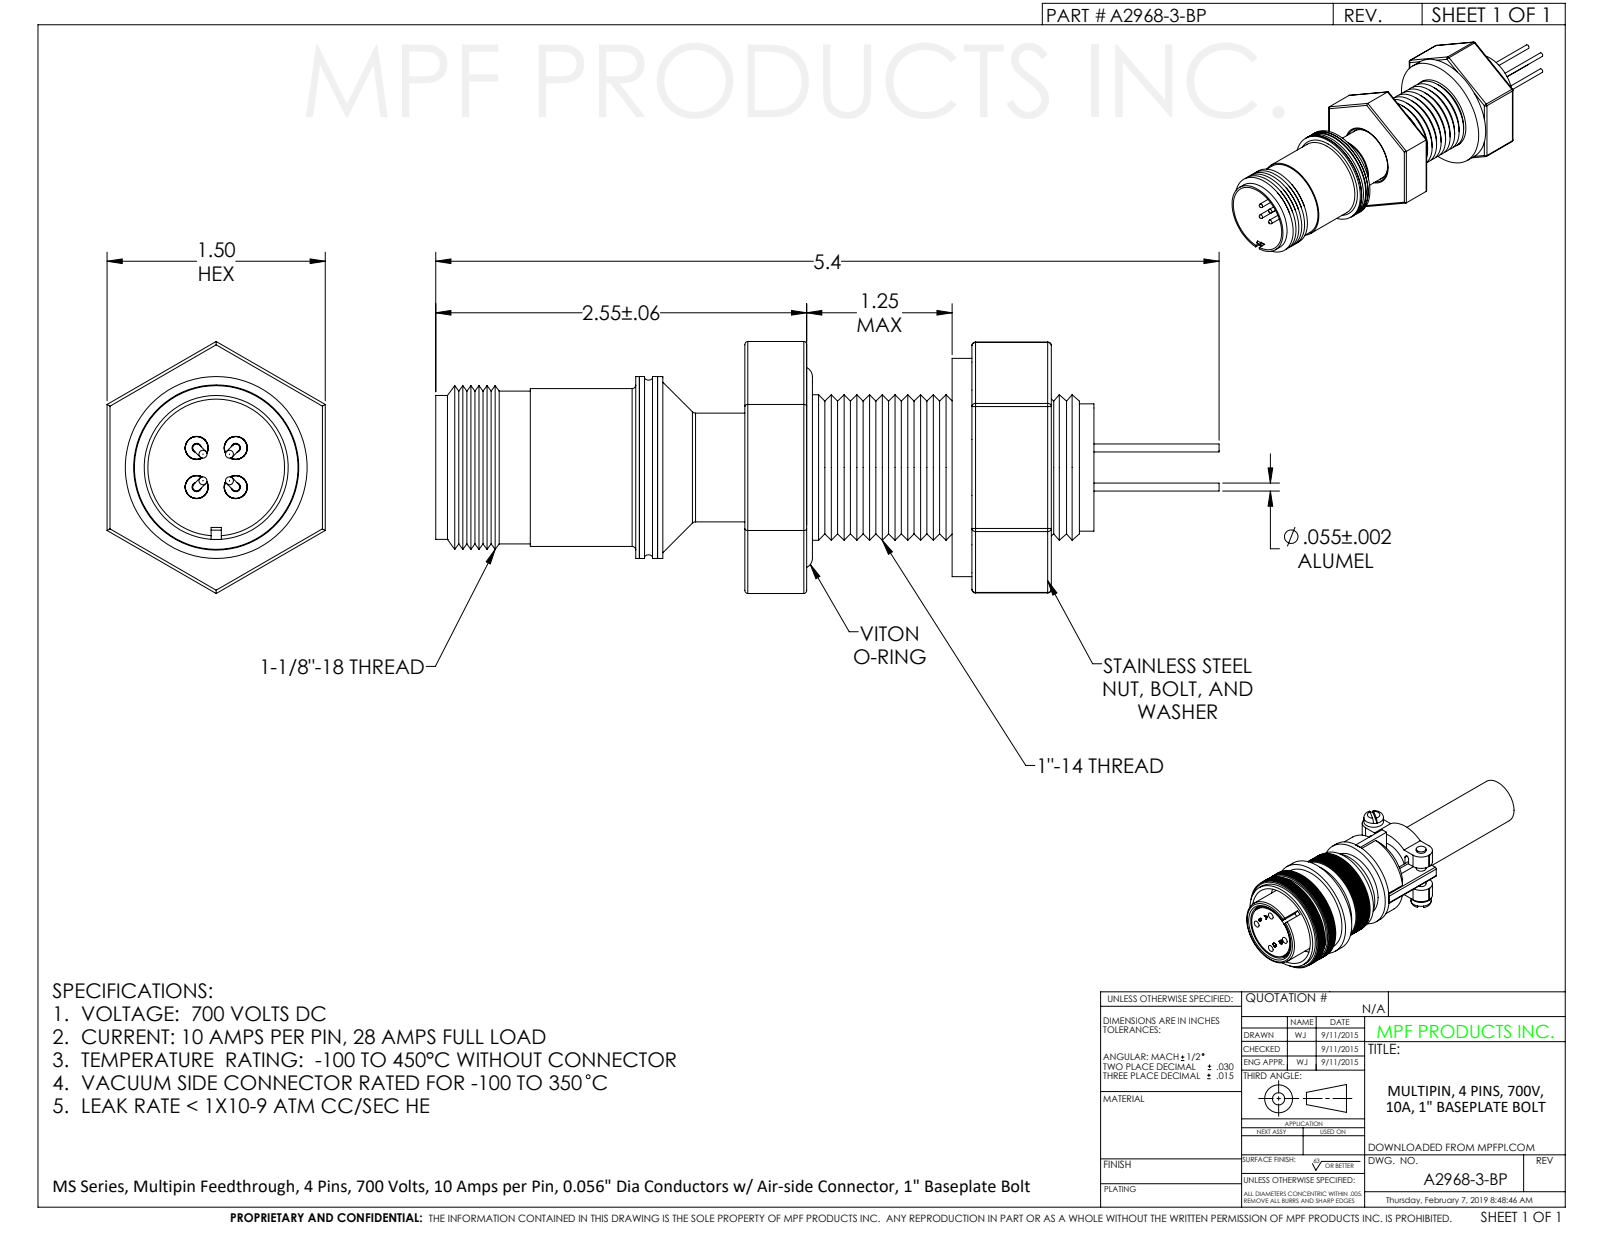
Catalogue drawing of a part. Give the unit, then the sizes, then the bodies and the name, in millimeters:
Units: millimetres
Overall size (bounding box): 167.1 × 44 × 38.1
Round holes (diameter × count): ⌀4 ×4, ⌀17.1 ×1, ⌀17.1 ×1, ⌀19.1 ×1, ⌀19.1 ×1, ⌀23.9 ×1, ⌀24.4 ×1, ⌀24.6 ×1, ⌀25.5 ×1, ⌀26.3 ×1, ⌀34.7 ×1
Round bosses / shafts (diameter × count): ⌀4.7 ×4, ⌀4.2 ×4, ⌀1.4 ×4, ⌀38.1 ×1, ⌀34.8 ×1, ⌀31.8 ×1, ⌀27.9 ×1, ⌀27.6 ×1
Partial cylindrical surfaces — rounded edges, fillets, slot ends (radius × count): R0.6 ×18, R0.5 ×12
Main face-to-face distances: 38.1, 39.6, 53.5, 13.9, 36.2, 3.5, 17.3, 2.5, 50.2, 15.2
Hole centre spacings: 6.4, 9.1, 11, 11.9, 2.7, 2.7, 4.8, 4.9
Volume: 45 330 mm³ · Surface area: 41 350 mm²
Bodies: 27 solids, 575 faces (175 planar, 192 cylindrical, 208 other)
Part name (STEP PRODUCT): A2968-3-BP
STEP written by: SolidWorks 2012 (CONFIG_CONTROL_DESIGN)
